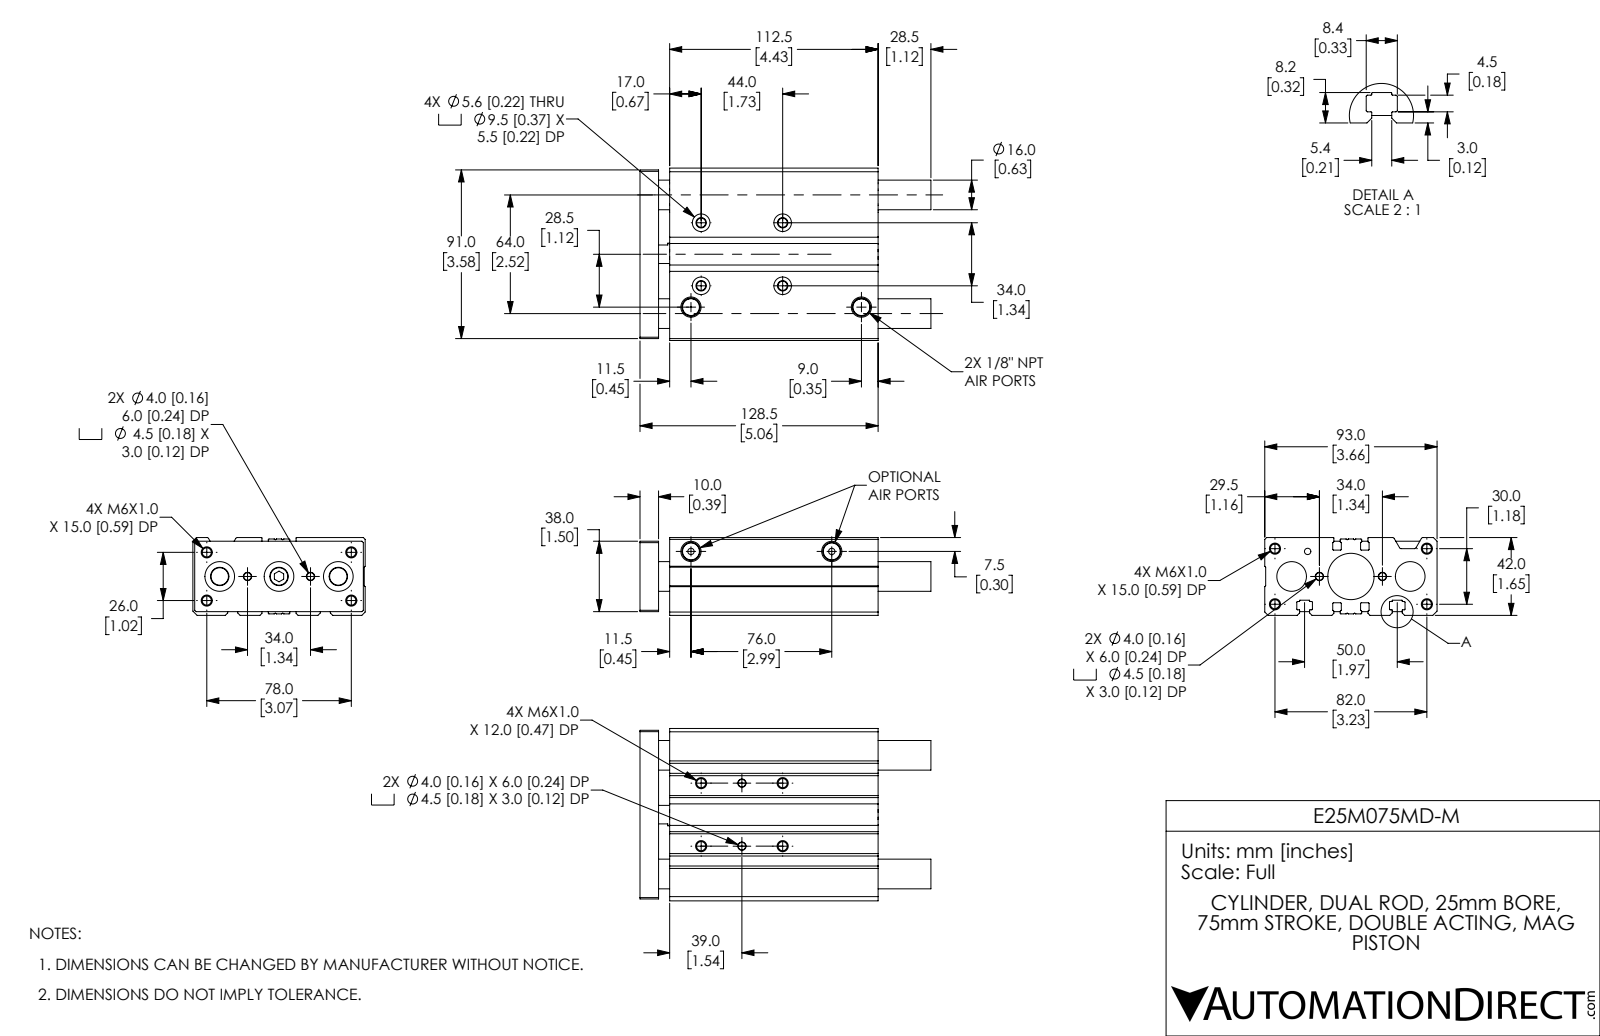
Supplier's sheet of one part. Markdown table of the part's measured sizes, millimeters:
| quantity | value |
| --- | --- |
| part name | E25M075MD-M; E25M075MD-M_ENDPLATE; E25M075MD-M_BODY |
| STEP written by | SolidWorks 2019 (CONFIG_CONTROL_DESIGN) |
| units | millimeters |
| bodies | 5 solids, 423 faces (139 planar, 190 cylindrical, 94 other) |
| overall size | 157 × 93 × 42 |
| volume | 409 681 mm³ |
| surface area | 107 823 mm² |
| round holes (diameter × count) | 4.92 × 8, 4 × 4, 4.5 × 4, 4.92 × 4, 5.6 × 4, 9.5 × 4, 8 × 3, 16 × 3, 3.43 × 2, 9.91 × 2, 3.43 × 1, 16 × 1 |
| round bosses / shafts (diameter × count) | 12 × 1, 9.91 × 1 |
| partial cylindrical surfaces (radius × count) | 0.2 × 32, 0.4 × 28, 1 × 4, 0.3 × 2 |
| main face-to-face distances | 42, 6, 93, 16, 10, 0.8, 2, 34.4, 15, 128.5 |
| hole center spacings | 2.83, 14.76, 17.49, 22, 25.55, 28.07, 28.3, 34 |
